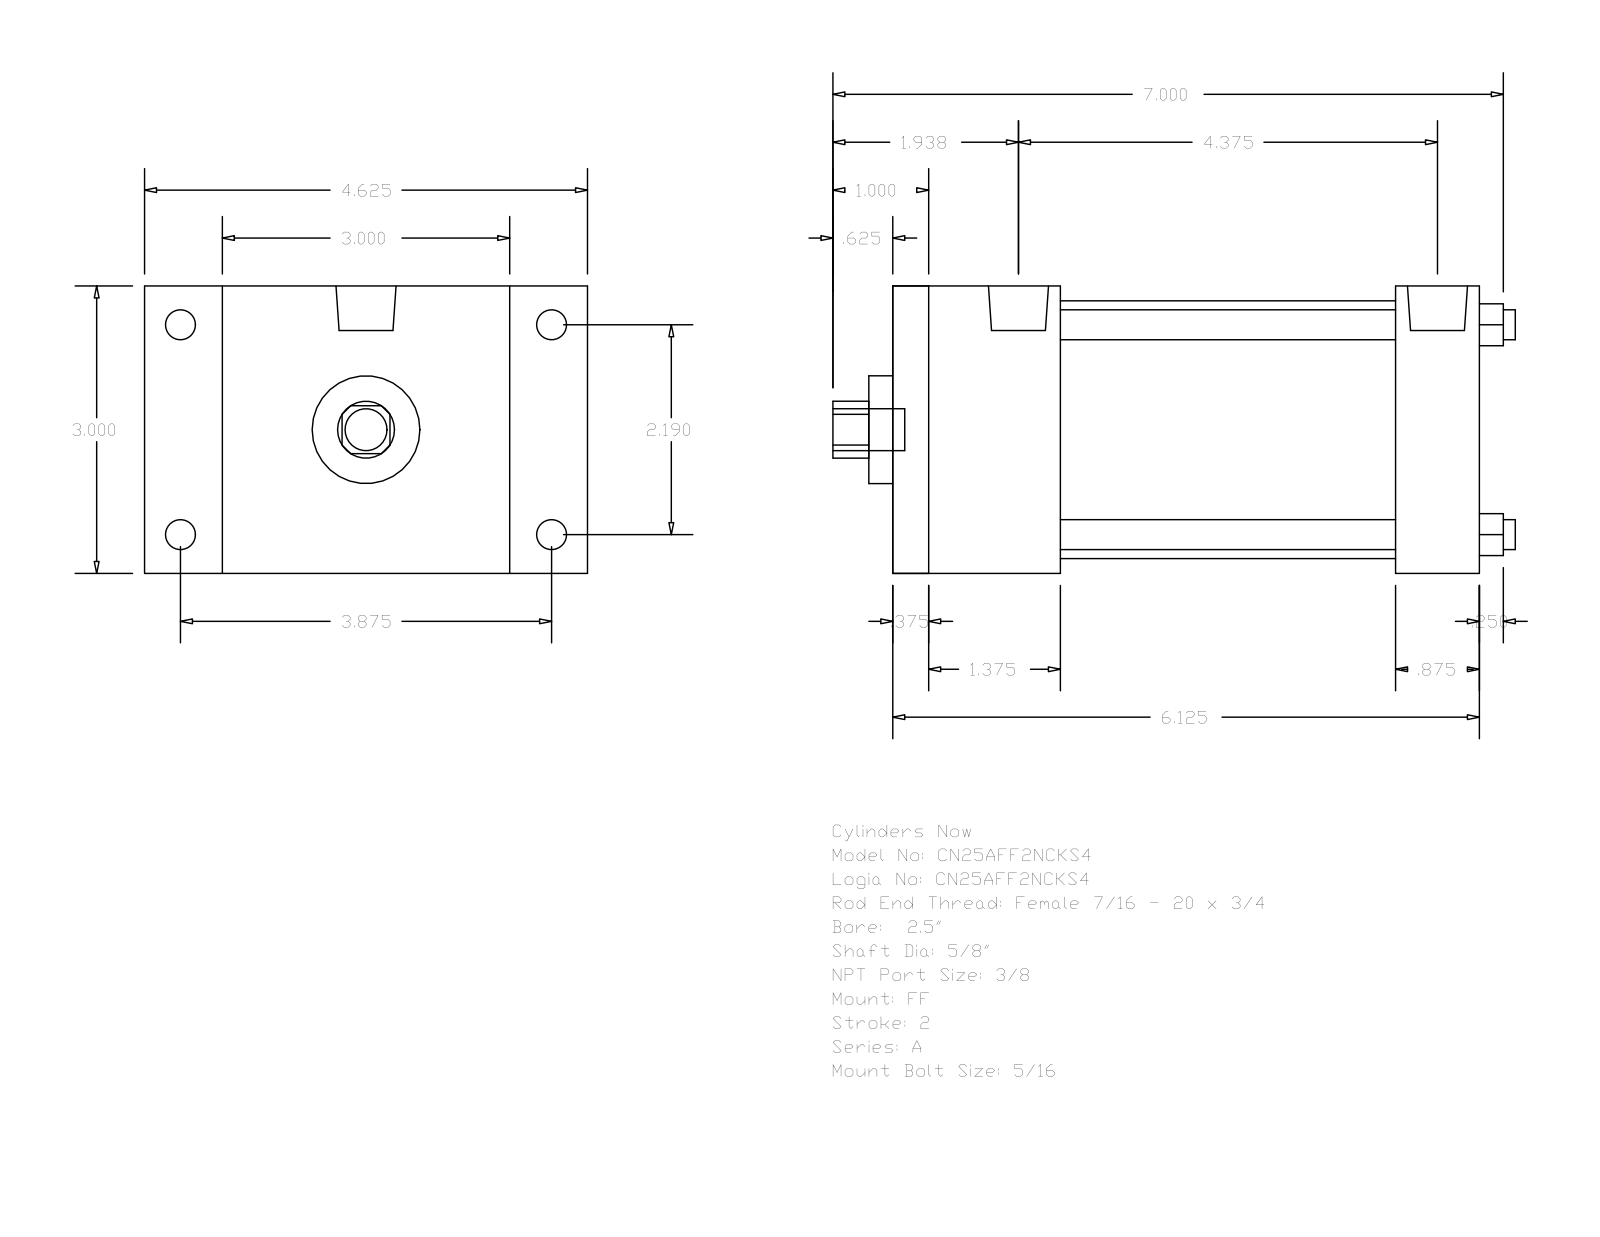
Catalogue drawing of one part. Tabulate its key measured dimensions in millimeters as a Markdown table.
| quantity | value |
| --- | --- |
| part name | A_FF__0250_0.625 |
| STEP written by | GSSL Pune (CONFIG_CONTROL_DESIGN) |
| units | millimeters |
| bodies | 0 solids, 92 faces (64 planar, 28 cylindrical, 0 other) |
| overall size | 180.97 × 117.47 × 76.2 |
| round holes (diameter × count) | 7.94 × 4, 15.88 × 1, 28.57 × 1, 68.33 × 1 |
| round bosses / shafts (diameter × count) | 7.94 × 4, 5.56 × 4, 15.93 × 2, 11.11 × 1 |
| partial cylindrical surfaces (radius × count) | 7.54 × 1 |
| main face-to-face distances | 76.2, 155.57, 9.52, 146.05, 44.45, 133.34, 34.93, 123.82, 88.89, 111.12 |
| hole center spacings | 39.33, 55.62, 78.66 |
